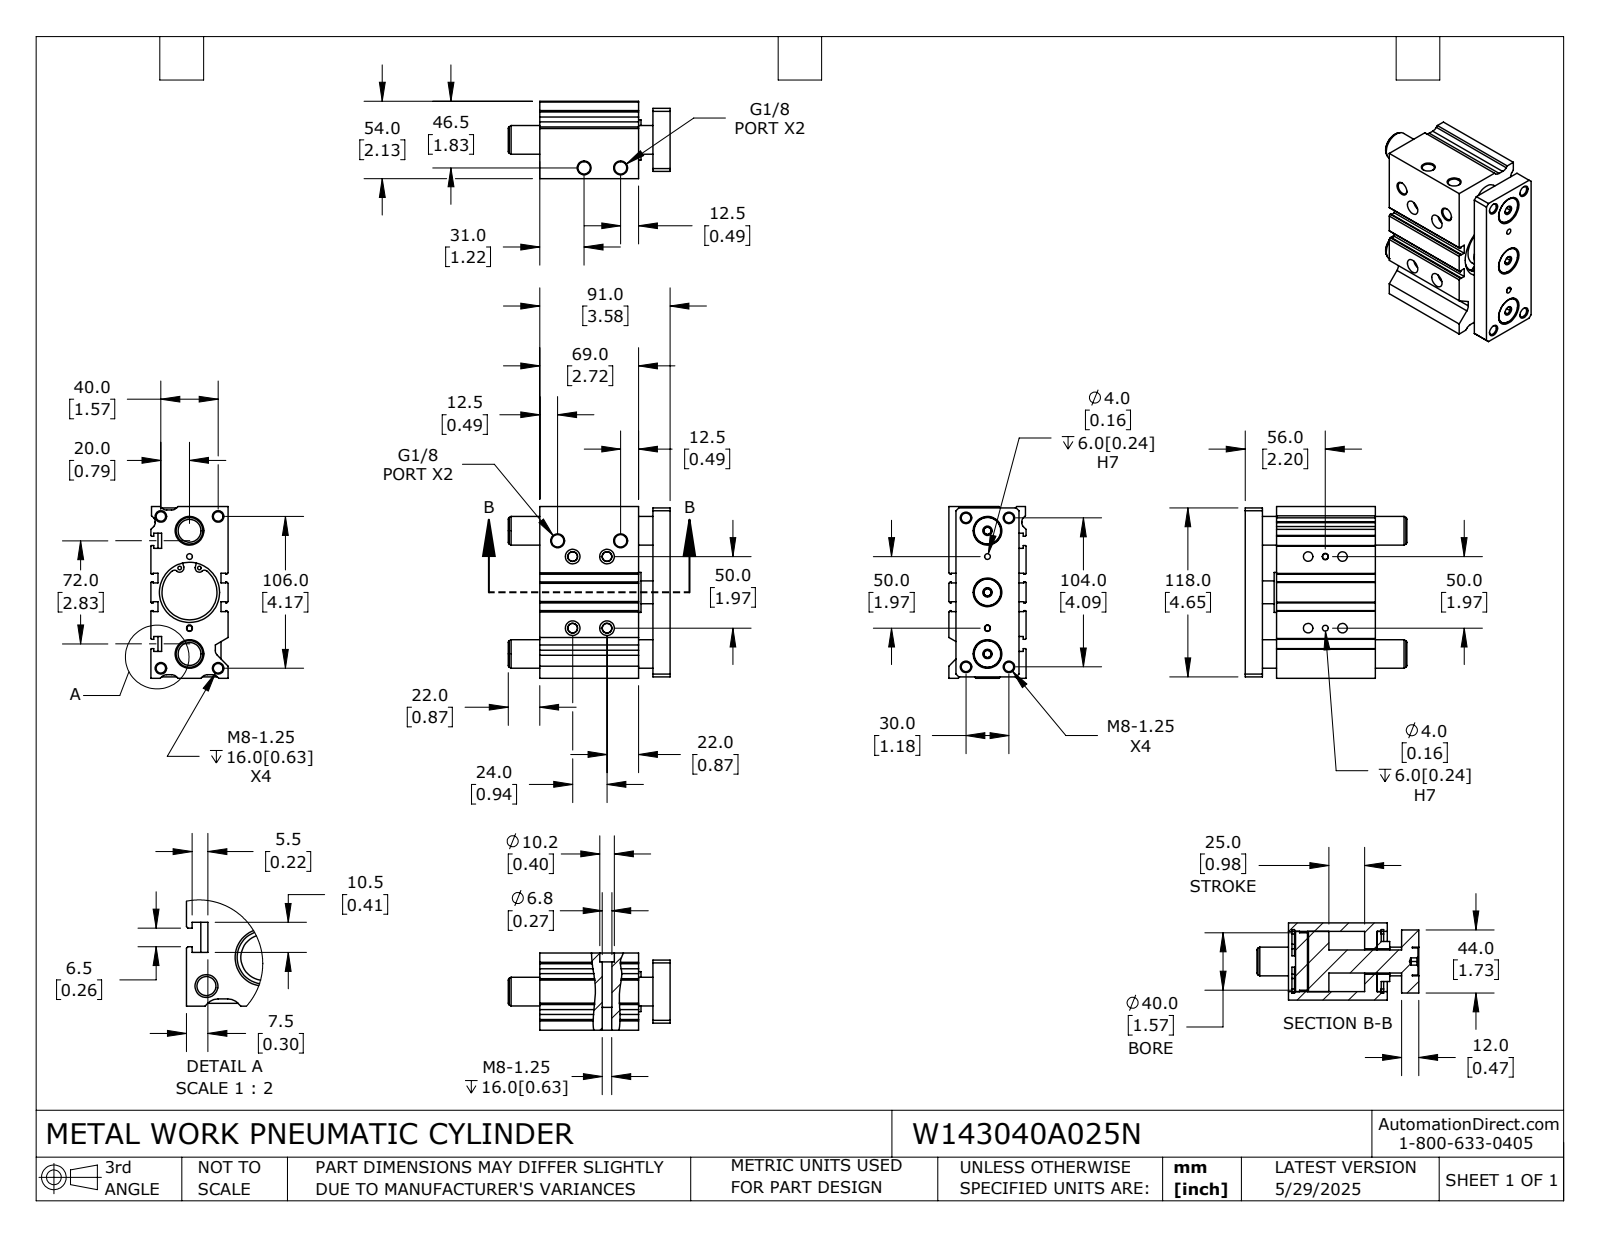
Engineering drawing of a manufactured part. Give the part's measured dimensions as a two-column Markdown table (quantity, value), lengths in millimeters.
| quantity | value |
| --- | --- |
| part name | W143040A025N_BODY; W143040A025N; W143040A025N_ROD |
| STEP written by | SolidWorks 2024 (CONFIG_CONTROL_DESIGN) |
| units | millimeters |
| bodies | 6 solids, 393 faces (192 planar, 151 cylindrical, 50 other) |
| overall size | 120 × 113 × 54 |
| volume | 443 600 mm³ |
| surface area | 112 200 mm² |
| round holes (diameter × count) | 6.7 × 12, 2.5 × 4, 4 × 4, 6.8 × 4, 8.6 × 4, 10.2 × 4, 5 × 3, 20 × 3, 17.7 × 1, 38.4 × 1 |
| round bosses / shafts (diameter × count) | 19 × 3, 44.5 × 2, 42 × 1, 40 × 1, 28 × 1, 16 × 1 |
| partial cylindrical surfaces (radius × count) | 5 × 7, 2 × 4, 2.3 × 4, 2.9 × 4, 4 × 2 |
| main face-to-face distances | 5, 54, 49, 22, 91, 12, 10, 79, 69, 2.5 |
| hole center spacings | 5.1, 10.5, 12, 17.5, 18.3, 22.4, 26.9, 30.9 |
